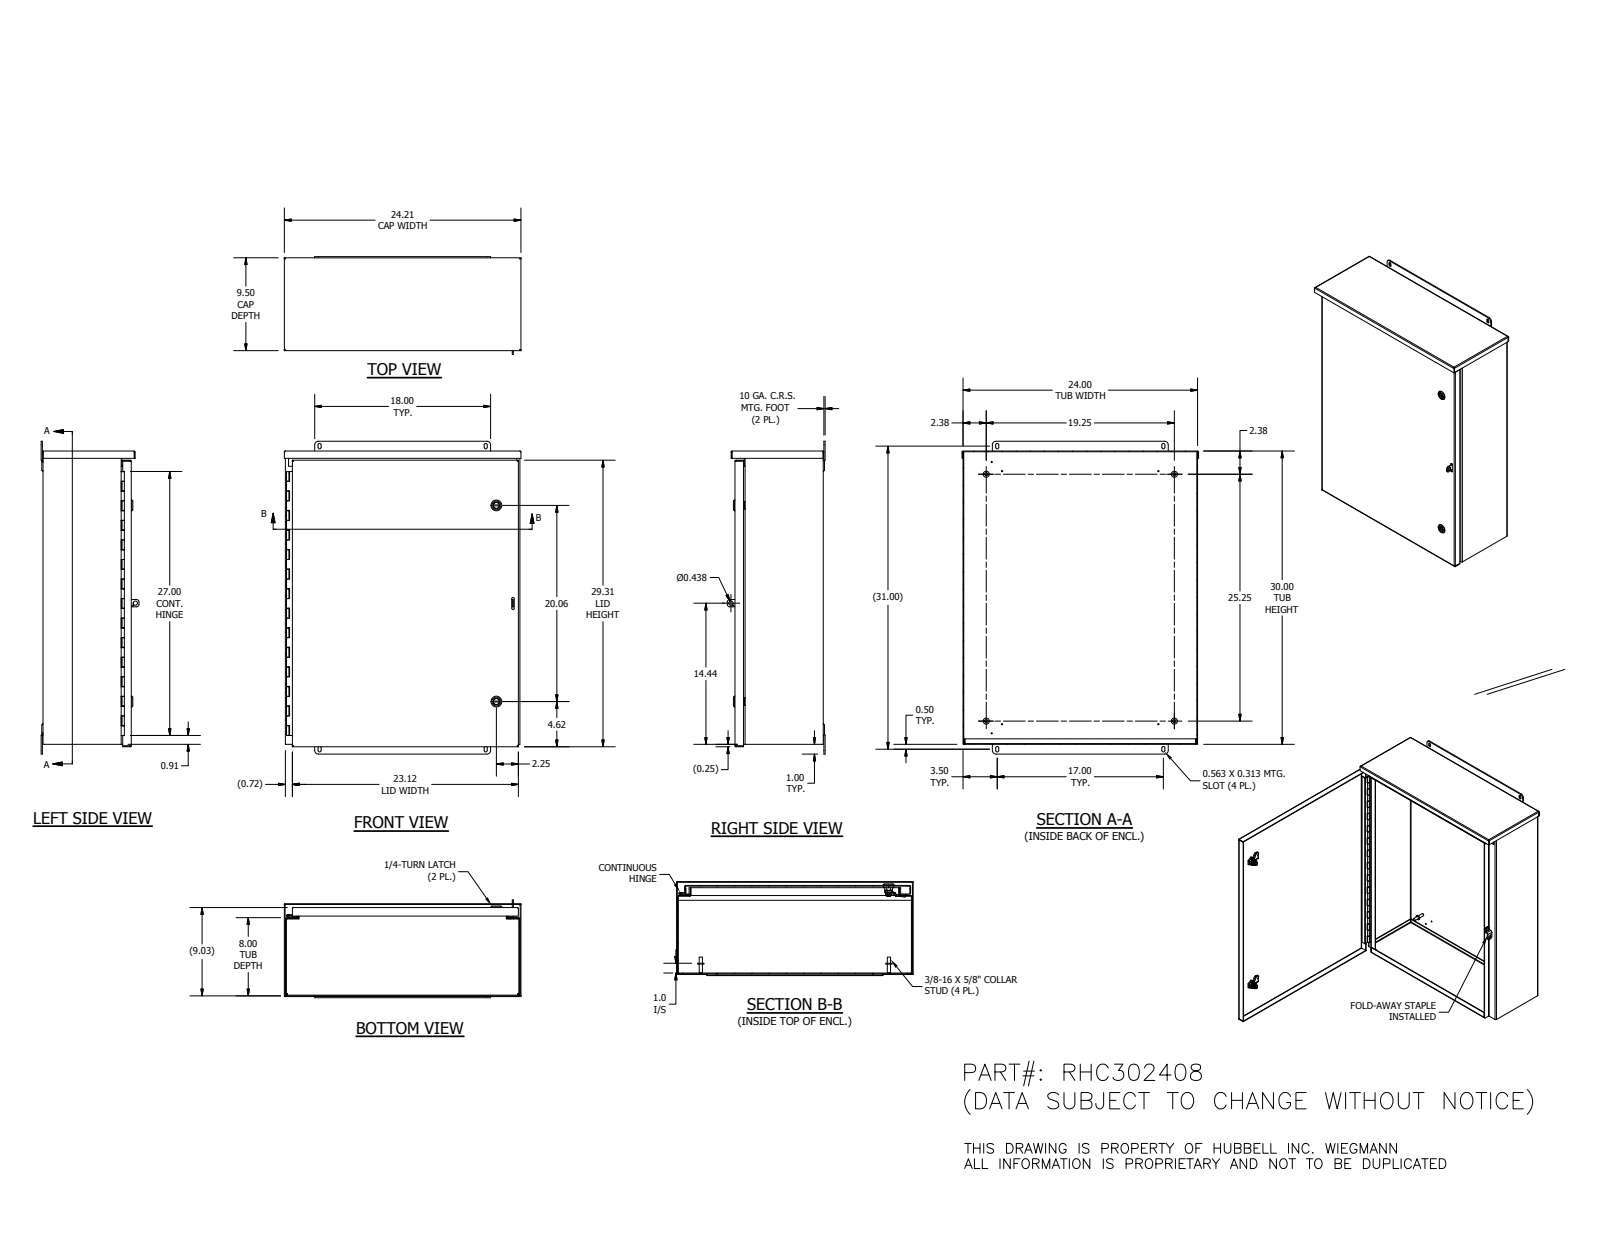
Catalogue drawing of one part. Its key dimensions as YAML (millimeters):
part_name: "RHC302408BLR; RHC24TOP; RHC2408BTM; RHC3024LID (+8 more)"
step_written_by: "Autodesk Inventor 2016 (AUTOMOTIVE_DESIGN)"
units: millimeters
bodies: {solids: 30, faces: 1420, planar: 813, cylindrical: 457, other: 150}
overall_size: [812.8, 614.95, 254.31]
volume: 3534000
surface_area: 3704000
round_holes:
  - {diameter: 3.05, count: 6}
  - {diameter: 3.17, count: 2}
  - {diameter: 5, count: 2}
  - {diameter: 8, count: 2}
  - {diameter: 10, count: 2}
  - {diameter: 10.2, count: 2}
  - {diameter: 16.1, count: 2}
  - {diameter: 20.38, count: 2}
  - {diameter: 5.03, count: 1}
  - {diameter: 5.11, count: 1}
  - {diameter: 11.11, count: 1}
round_bosses_or_shafts:
  - {diameter: 15.88, count: 4}
  - {diameter: 8.38, count: 4}
  - {diameter: 28, count: 2}
  - {diameter: 27, count: 2}
  - {diameter: 23, count: 2}
  - {diameter: 19.8, count: 2}
  - {diameter: 15.8, count: 2}
  - {diameter: 15.2, count: 2}
partial_cylinders:
  - {radius: 0.3, count: 56}
  - {radius: 0.5, count: 21}
  - {radius: 3.47, count: 13}
  - {radius: 1.59, count: 11}
  - {radius: 3.17, count: 10}
  - {radius: 0.79, count: 8}
  - {radius: 2.67, count: 8}
  - {radius: 3.97, count: 8}
face_to_face_distances: [1.88, 227.57, 229.45, 225.69, 607.72, 760.12, 605.84, 609.6, 758.24, 762]
hole_center_spacings: [35.91, 406.4, 433.98, 657.35, 681.63, 772.83, 807.26, 8.98]
